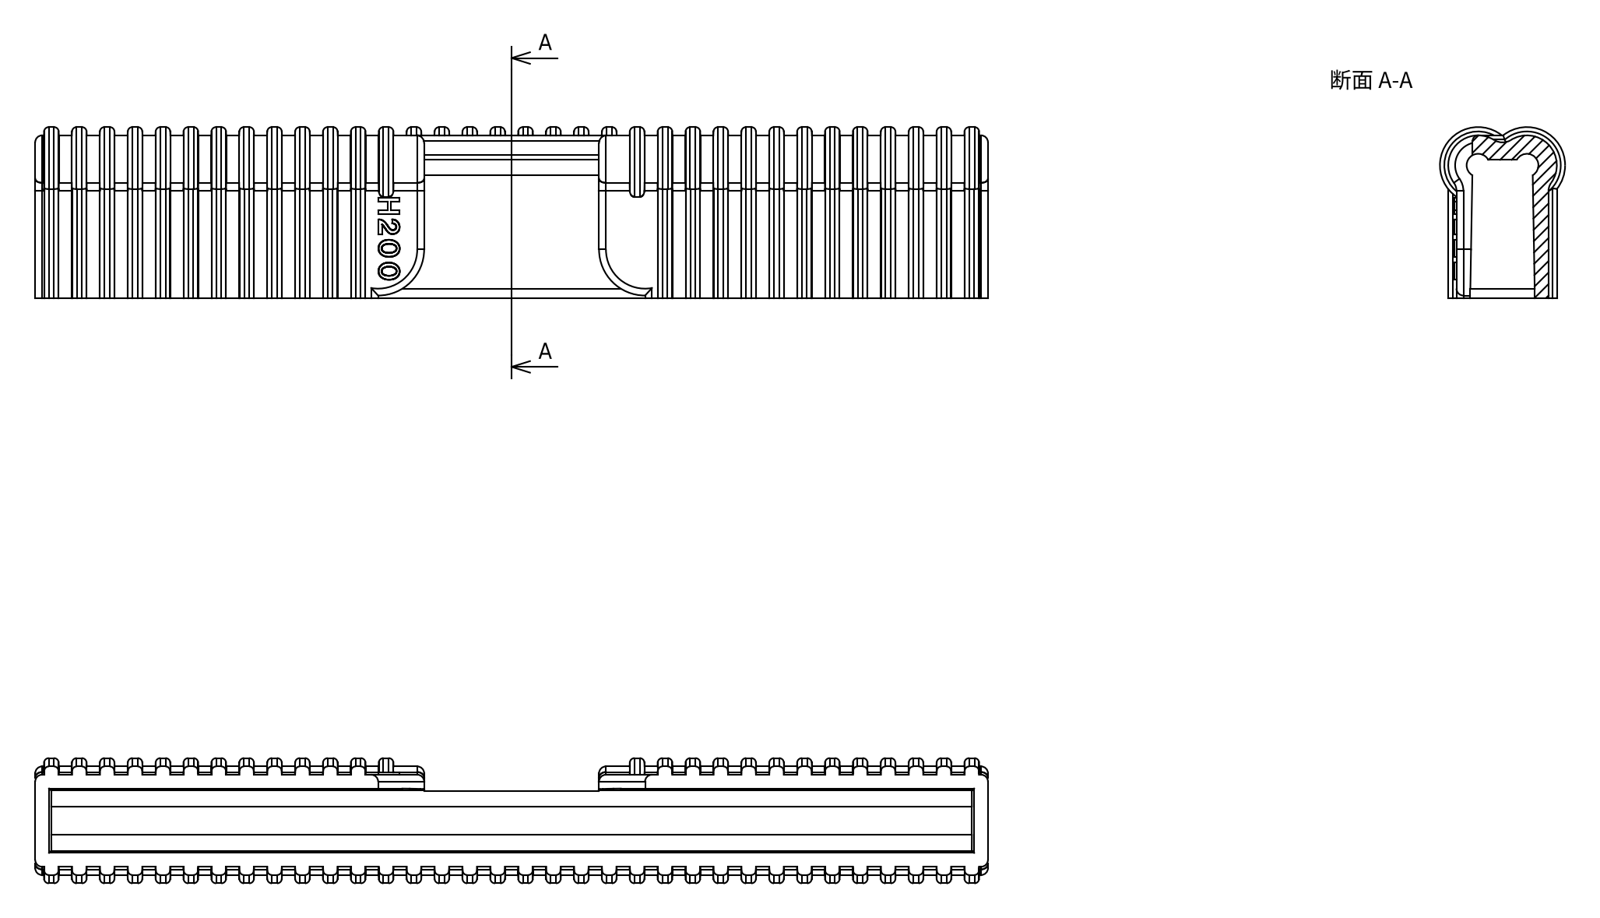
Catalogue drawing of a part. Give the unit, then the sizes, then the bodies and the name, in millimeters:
Units: millimetres
Overall size (bounding box): 207 × 37.1 × 27.2
Partial cylindrical surfaces — rounded edges, fillets, slot ends (radius × count): R1 ×184, R1.5 ×8, R2.5 ×2, R3 ×2, R6.5 ×2, R8.3 ×2, R10 ×2, R1.11 ×1
Main face-to-face distances: 20, 21.8, 1.8, 30, 3.01, 4.81, 18.79, 16.99, 23.6, 207
Volume: 73 313 mm³ · Surface area: 43 358 mm²
Bodies: 6 solids, 1103 faces (422 planar, 419 cylindrical, 262 other)
STEP written by: XStep 1.0 (CONFIG_CONTROL_DESIGN)
